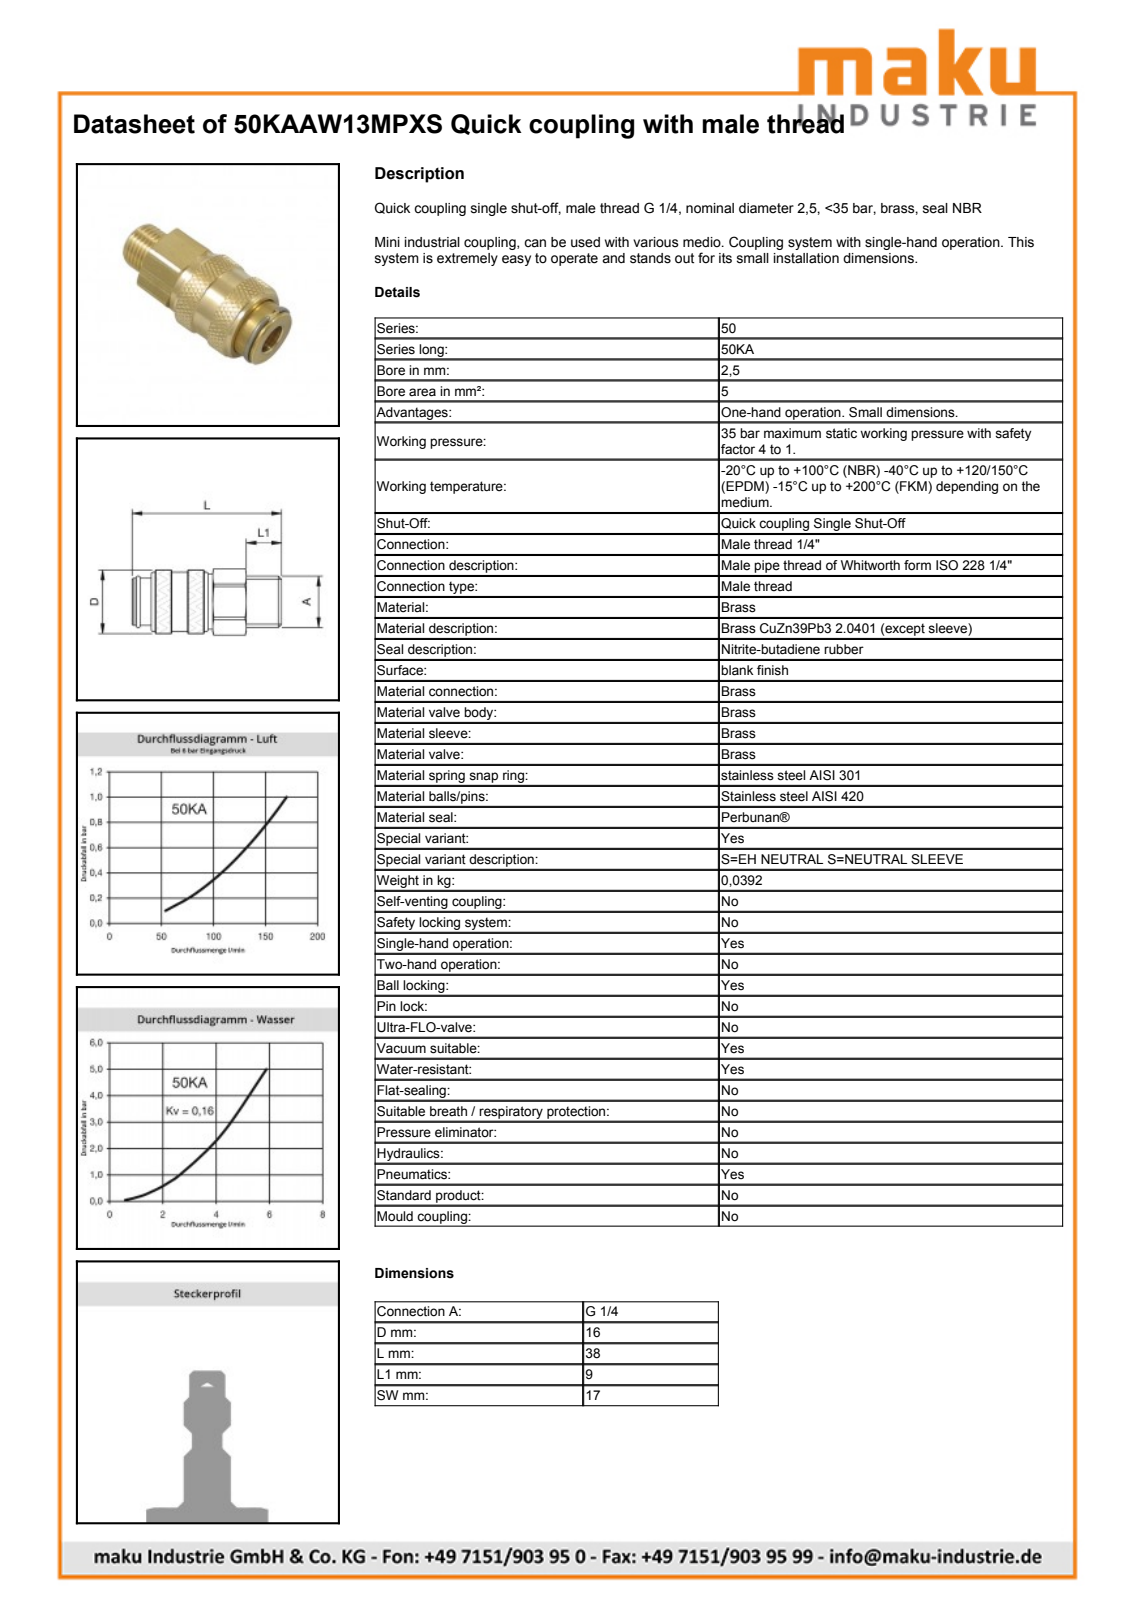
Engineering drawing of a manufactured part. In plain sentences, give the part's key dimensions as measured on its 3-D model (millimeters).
The part is named "D109125". Its 3-D file was written by "Autodesk Inventor 2013 (AUTOMOTIVE_DESIGN)". It is 2 solids with 75 faces: 19 planar, 25 cylindrical and 31 other. Overall it measures 37.79 by 18.96 by 18.34 millimeters. Its volume is 6 505 cubic millimeters and its surface area 3 692 square millimeters. Round holes: 1 of diameter 11.46, 1 of diameter 12.15, 1 of diameter 14. Round bosses or shafts: 1 of diameter 16.15, 1 of diameter 15.1, 1 of diameter 13.16, 1 of diameter 12, 1 of diameter 11.4, 1 of diameter 11.15. Partial cylindrical surfaces (rounded edges, fillets, slot ends): 1 of radius 4.08, 1 of radius 9.57. The main face-to-face distances are 17, 37.79, 28.79, 9, 17.02, 20.24, 8.55, 17.55, 15.79, 4.45.
